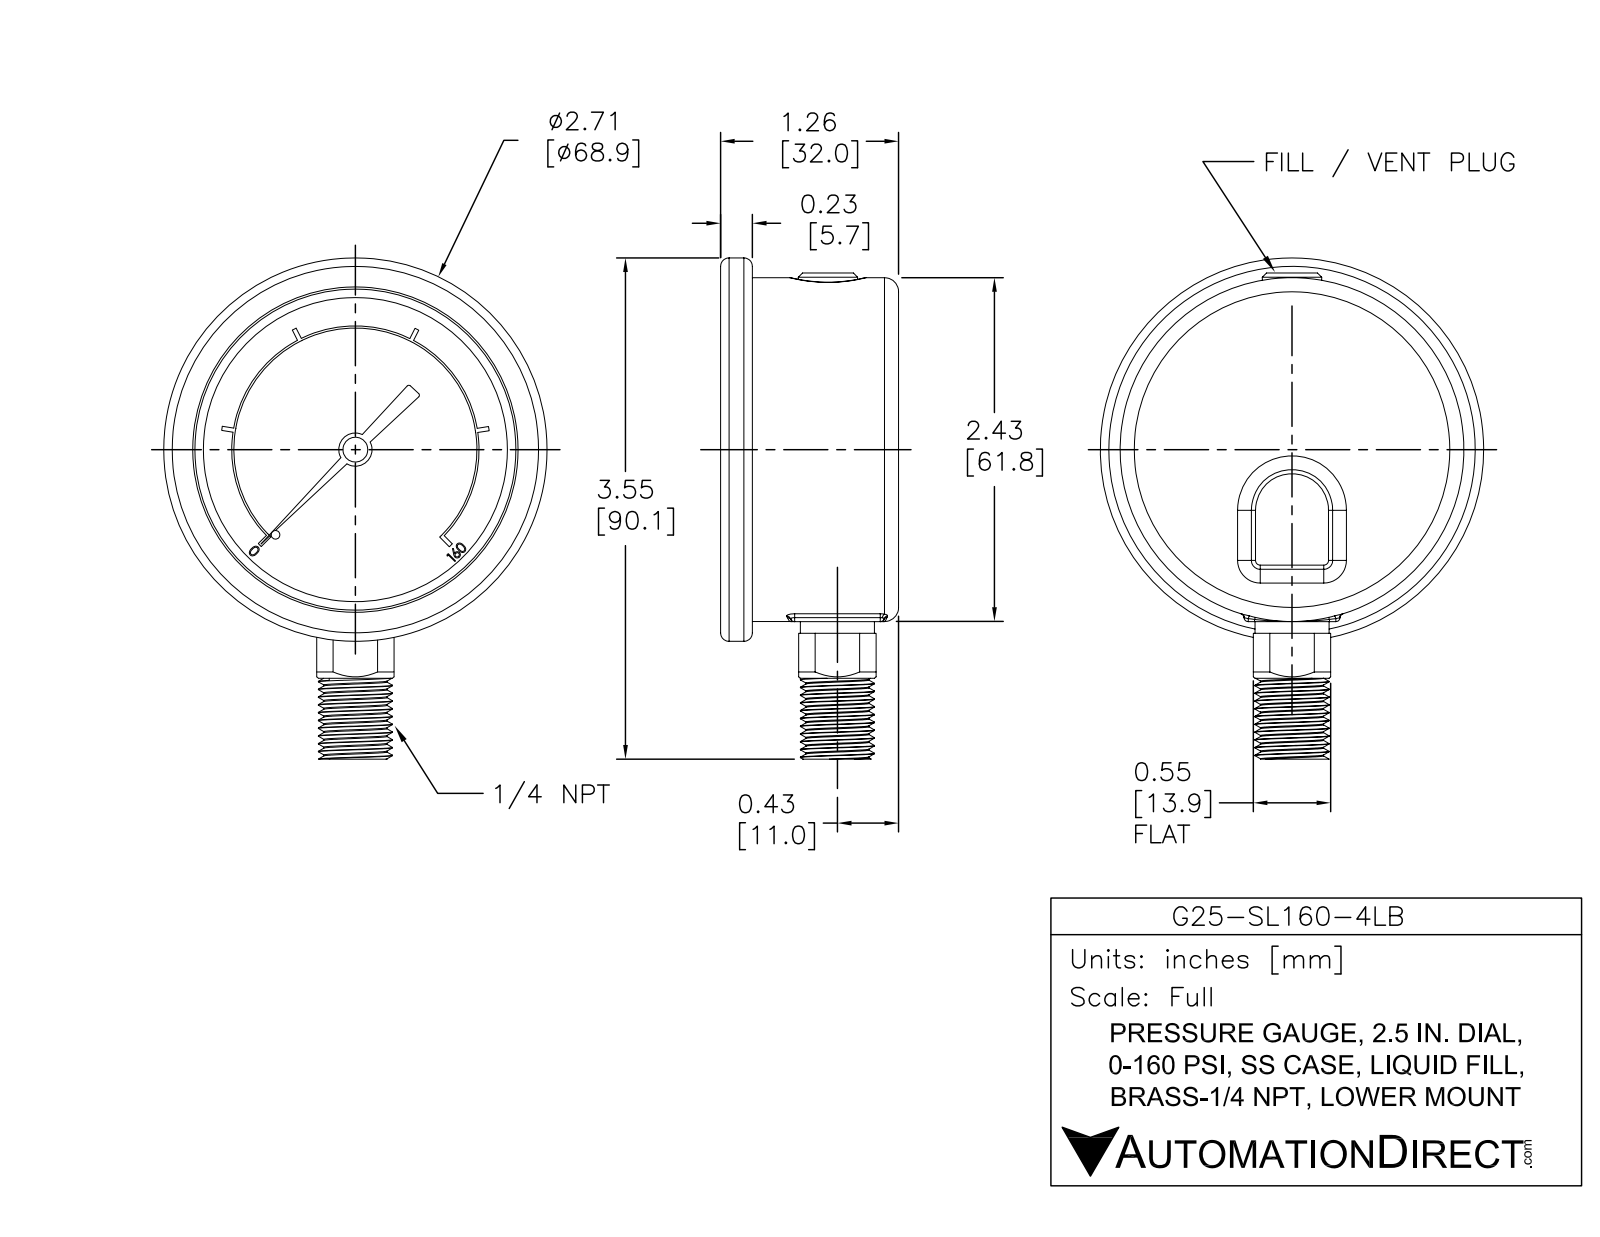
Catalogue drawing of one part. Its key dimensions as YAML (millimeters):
part_name: "G25-SL160-4LB"
step_written_by: "SolidWorks 2021 (AUTOMOTIVE_DESIGN)"
units: millimeters
bodies: {solids: 1, faces: 346, planar: 198, cylindrical: 85, other: 63}
overall_size: [90.1, 68.9, 32]
volume: 86410
surface_area: 15920
round_holes:
  - {diameter: 0.7, count: 1}
  - {diameter: 1.8, count: 1}
  - {diameter: 3, count: 1}
  - {diameter: 57.7, count: 1}
round_bosses_or_shafts:
  - {diameter: 68.9, count: 1}
  - {diameter: 61.8, count: 1}
  - {diameter: 13.3, count: 1}
  - {diameter: 10.7, count: 1}
  - {diameter: 6, count: 1}
  - {diameter: 4.5, count: 1}
  - {diameter: 3.6, count: 1}
  - {diameter: 1, count: 1}
partial_cylinders:
  - {radius: 0.8, count: 9}
  - {radius: 2.5, count: 3}
  - {radius: 0.4, count: 2}
  - {radius: 8, count: 1}
  - {radius: 21.8, count: 1}
  - {radius: 22.2, count: 1}
face_to_face_distances: [25.7, 32, 6.4, 26.3, 0.6, 5.7, 2.5, 23.1, 23.7, 29.5]
hole_center_spacings: [1.7]
